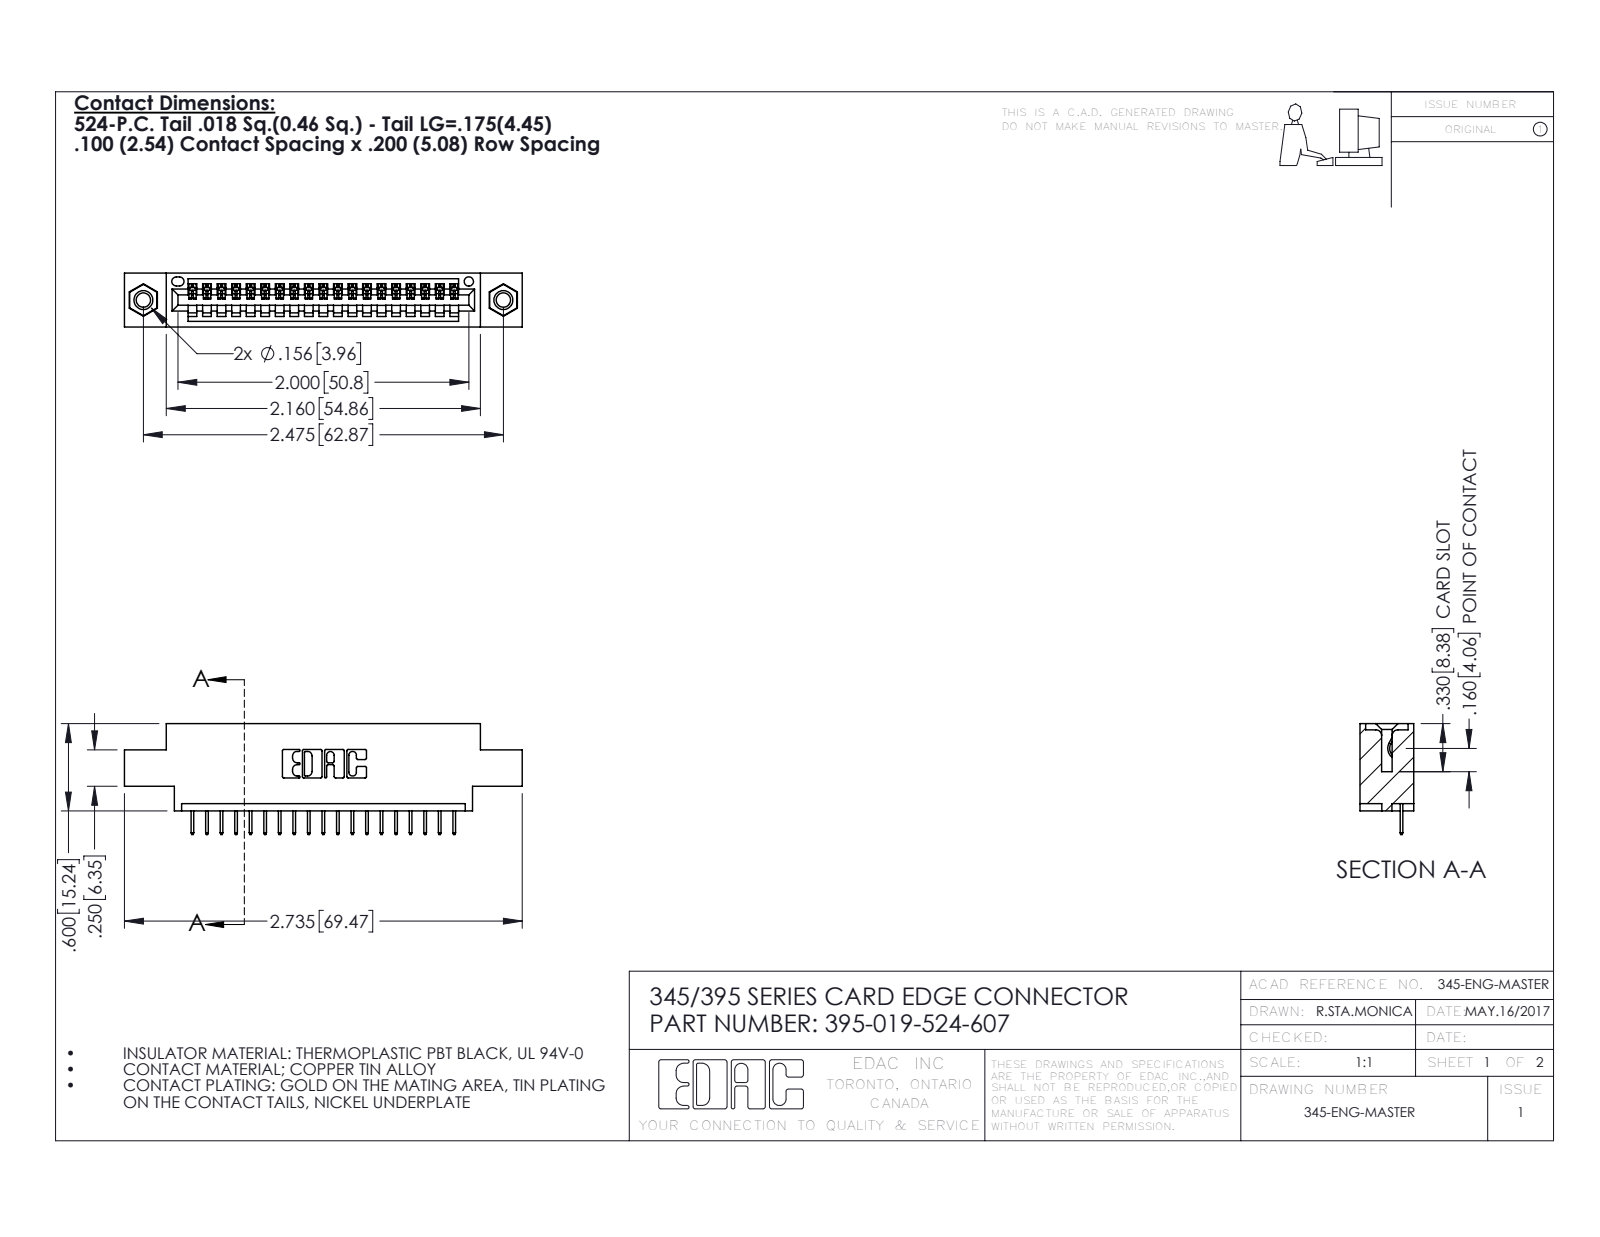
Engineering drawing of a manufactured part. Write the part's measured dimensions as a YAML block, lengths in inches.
part_name: "345-292-001_345-293-124; 395-019-524-607; 345-250-001_345-250-005-103; 345 Part_0.170 Offset - 0.156 Dia-TI"
step_written_by: "SolidWorks 2016 (CONFIG_CONTROL_DESIGN)"
units: inches
bodies: {solids: 22, faces: 1368, planar: 990, cylindrical: 362, other: 16}
overall_size: [2.735, 0.762, 0.37]
volume: 0.379
surface_area: 12.18
round_holes:
  - {diameter: 0.098, count: 2}
  - {diameter: 0.125, count: 2}
  - {diameter: 0.156, count: 2}
  - {diameter: 0.064, count: 1}
round_bosses_or_shafts:
  - {diameter: 0.155, count: 2}
partial_cylinders:
  - {radius: 0.006, count: 38}
  - {radius: 0.01, count: 22}
  - {radius: 0.007, count: 6}
  - {radius: 0.031, count: 6}
  - {radius: 0.026, count: 3}
  - {radius: 0.031, count: 2}
  - {radius: 0.04, count: 2}
  - {radius: 0.014, count: 1}
face_to_face_distances: [0.37, 0.072, 0.298, 0.2, 0.098, 0.272, 0.025, 0.225, 0.1, 0.072]
hole_center_spacings: [0.27, 2.241, 2.475]
